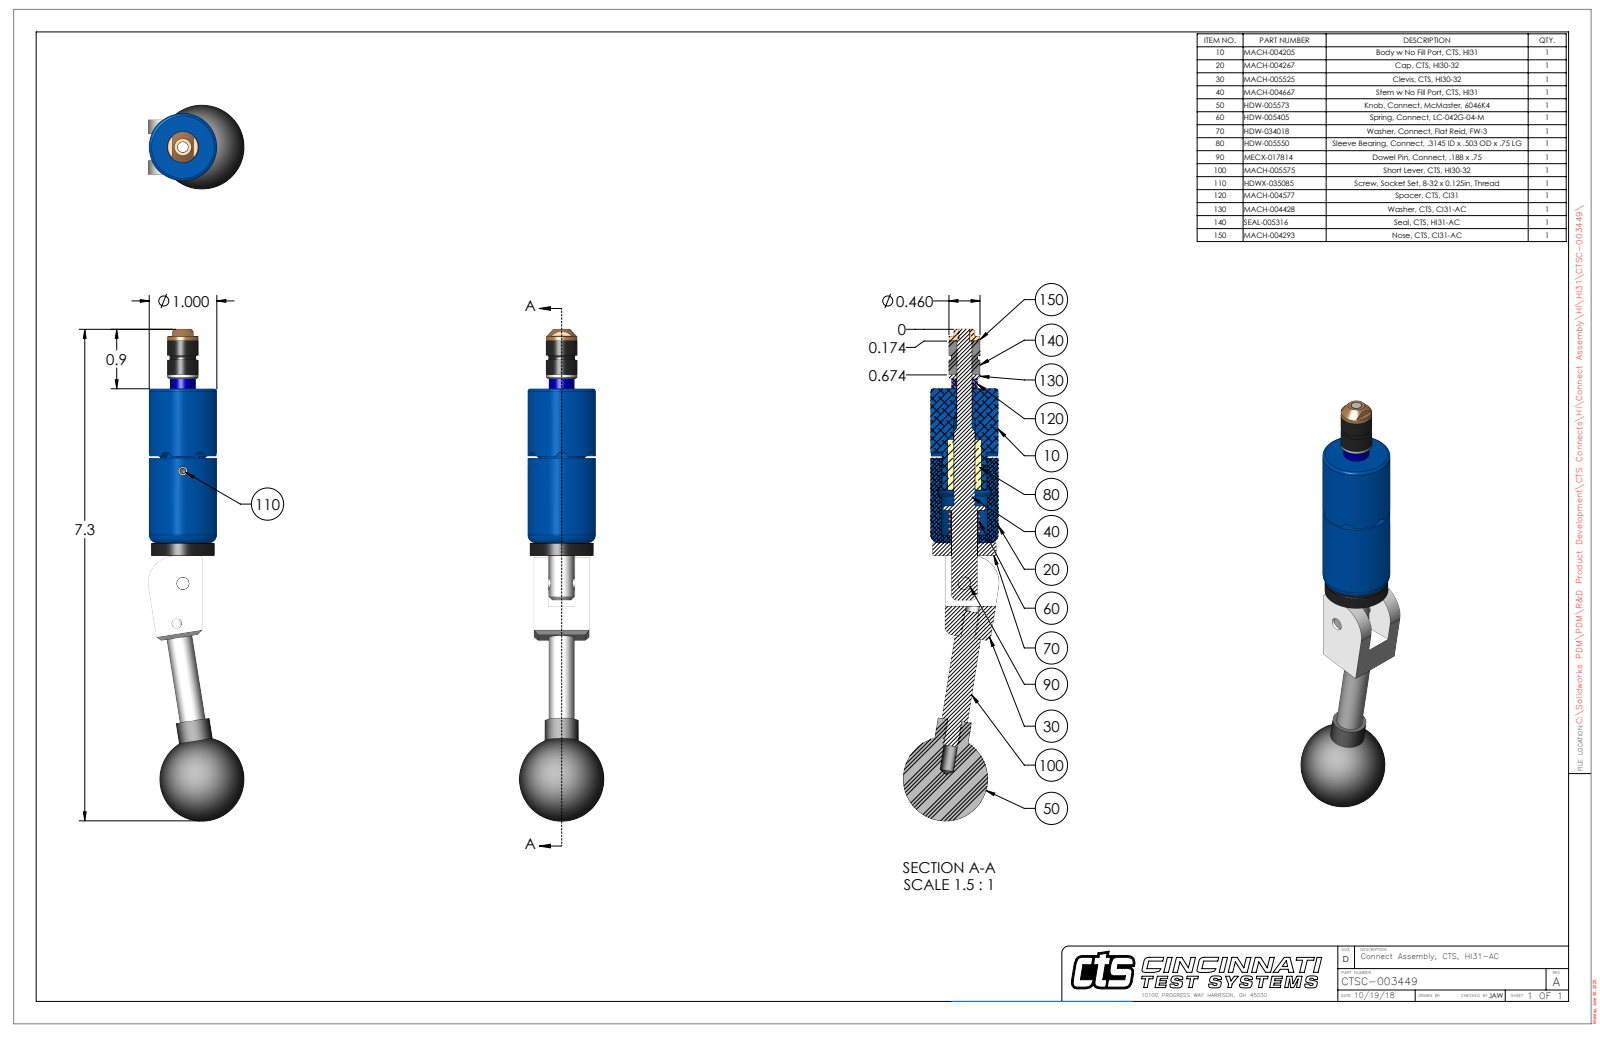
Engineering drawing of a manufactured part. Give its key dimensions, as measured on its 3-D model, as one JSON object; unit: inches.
{"part_name": "CTSC-003449", "step_written_by": "SolidWorks 2023 (AUTOMOTIVE_DESIGN)", "units": "inches", "bodies": {"solids": 10, "faces": 253, "planar": 98, "cylindrical": 98, "other": 57}, "overall_size": [7.268, 1.416, 1.25], "volume_in3": 3.782, "surface_area_in2": 30.83, "round_holes": [[0.201, 2], [0.136, 1], [0.15, 1], [0.159, 1], [0.189, 1], [0.218, 1], [0.228, 1], [0.229, 1], [0.385, 1], [0.392, 1]], "round_bosses_or_shafts": [[1, 1], [0.936, 1], [0.5, 1], [0.462, 1], [0.46, 1], [0.38, 1], [0.379, 1], [0.375, 1]], "partial_cylinders_radius": [[0.093, 6], [0.029, 2], [0.344, 1], [0.4, 1], [0.482, 1]], "face_to_face_distances": [0.21, 0.602, 0.812, 0.187, 2.28, 2.467, 0.391, 1.026, 1.253, 1.441], "hole_center_spacings": [0.599, 1.658, 2.252]}
